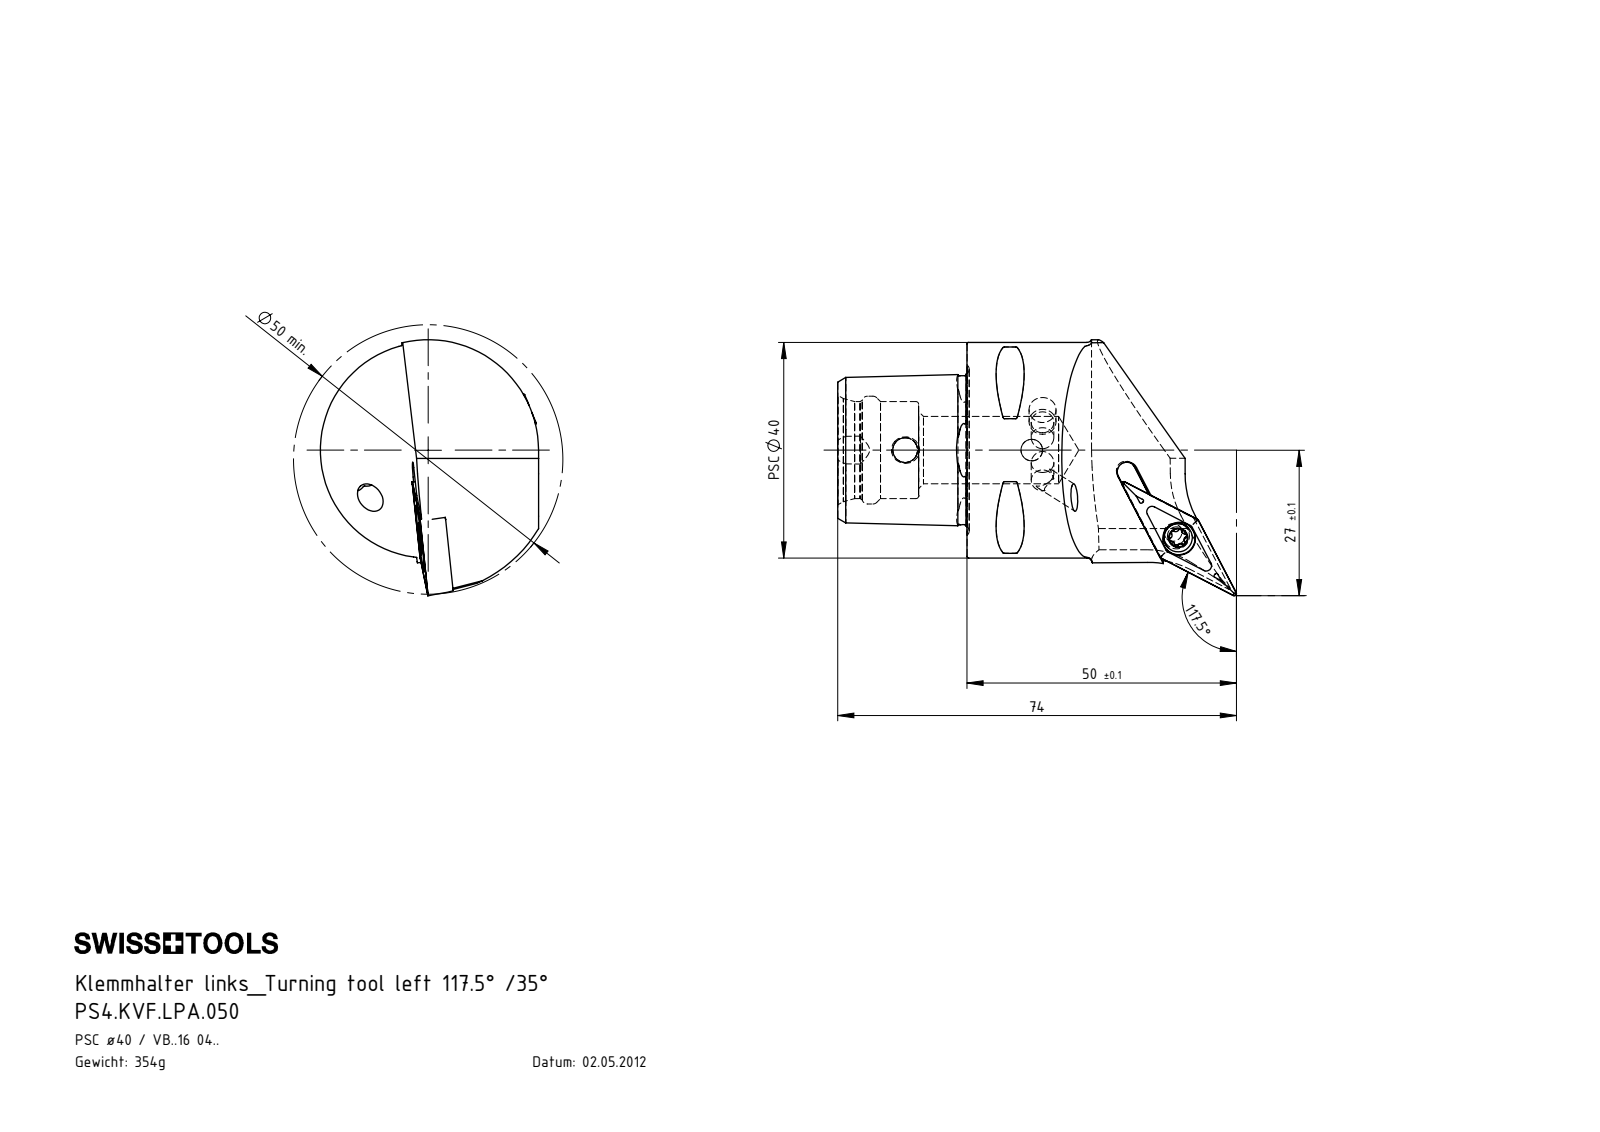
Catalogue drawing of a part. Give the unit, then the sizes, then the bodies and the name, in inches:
Units: inches
Overall size (bounding box): 2.913 × 1.87 × 1.594
Round holes (diameter × count): ⌀0.165 ×2, ⌀0.197 ×2, ⌀0.13 ×1, ⌀0.157 ×1, ⌀0.173 ×1, ⌀0.181 ×1, ⌀0.24 ×1, ⌀0.492 ×1, ⌀0.709 ×1, ⌀0.787 ×1
Round bosses / shafts (diameter × count): ⌀1.575 ×1, ⌀0.236 ×1, ⌀0.207 ×1, ⌀0.157 ×1
Partial cylindrical surfaces — rounded edges, fillets, slot ends (radius × count): R0.012 ×8, R0.013 ×6, R0.023 ×6, R0.006 ×2, R0.669 ×2, R0.031 ×1, R0.069 ×1, R0.118 ×1
Main face-to-face distances: 0.945, 0.175, 0.611, 0.175, 1.39, 0.354, 0.591, 0.187, 0.187, 0.012
Hole centre spacings: 0.925
Volume: 2.725 in³ · Surface area: 19.88 in²
Bodies: 5 solids, 214 faces (56 planar, 50 cylindrical, 108 other)
Part name (STEP PRODUCT): PS4.KVF.LPA.050; KVT_MB_600_060; PS4-KVF.LPA.050_A; VBMT160404 (+1 more)
STEP written by: SolidWorks 2017 (AUTOMOTIVE_DESIGN)
